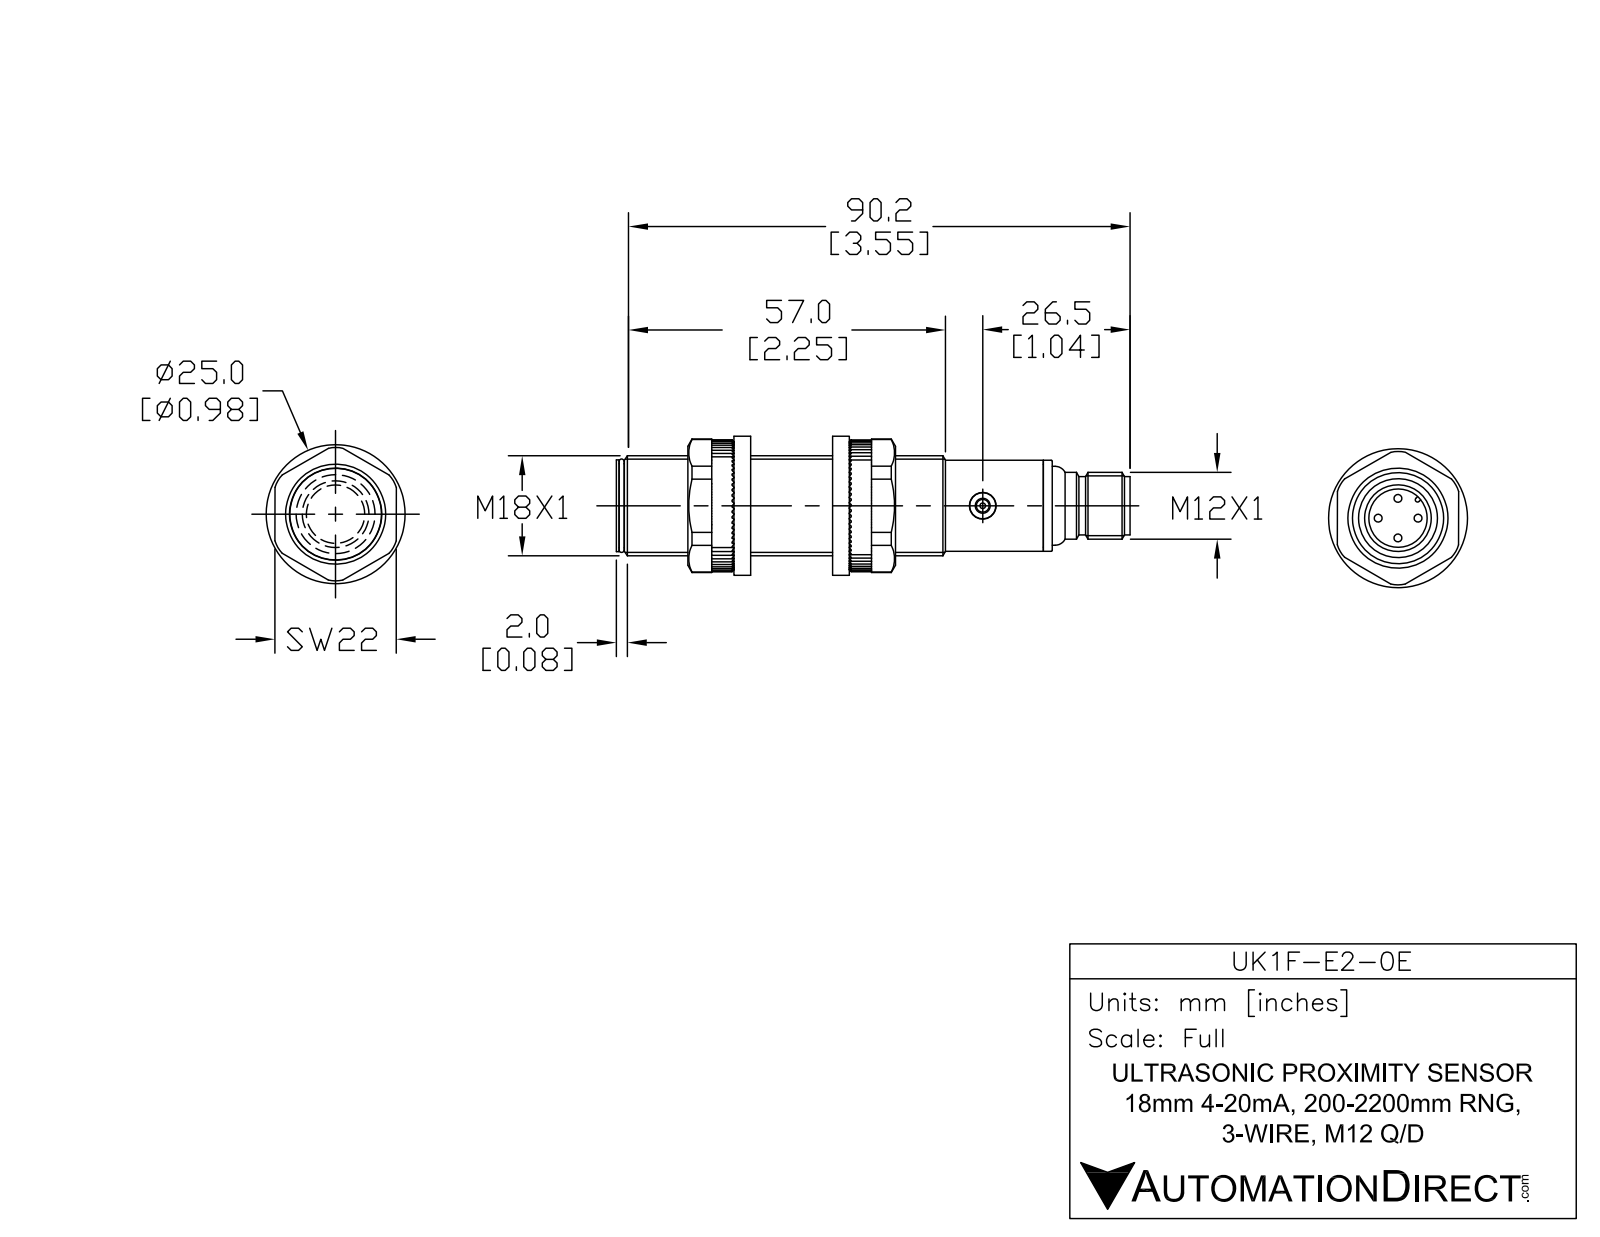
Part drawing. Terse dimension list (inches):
name: UK1F-E2-0E
written by: SolidWorks 2017 (AUTOMOTIVE_DESIGN)
unit: in
bodies: 6 solids, 106 faces (21 planar, 48 cylindrical, 37 other)
size: 3.606 × 0.709 × 0.709
volume: 1.202 in³; area: 10.68 in²
holes: 1× ⌀0.106, 1× ⌀0.185, 1× ⌀0.276, 1× ⌀0.327, 1× ⌀0.374
bosses: 4× ⌀0.039, 1× ⌀0.709, 1× ⌀0.654, 1× ⌀0.646, 1× ⌀0.622, 1× ⌀0.559, 1× ⌀0.472, 1× ⌀0.413
rounds: 1× R0.024
face distances: 2.957, 0.039, 2.996, 0.037, 2.994, 0.043, 0.157, 3.055, 3.053, 3.016
